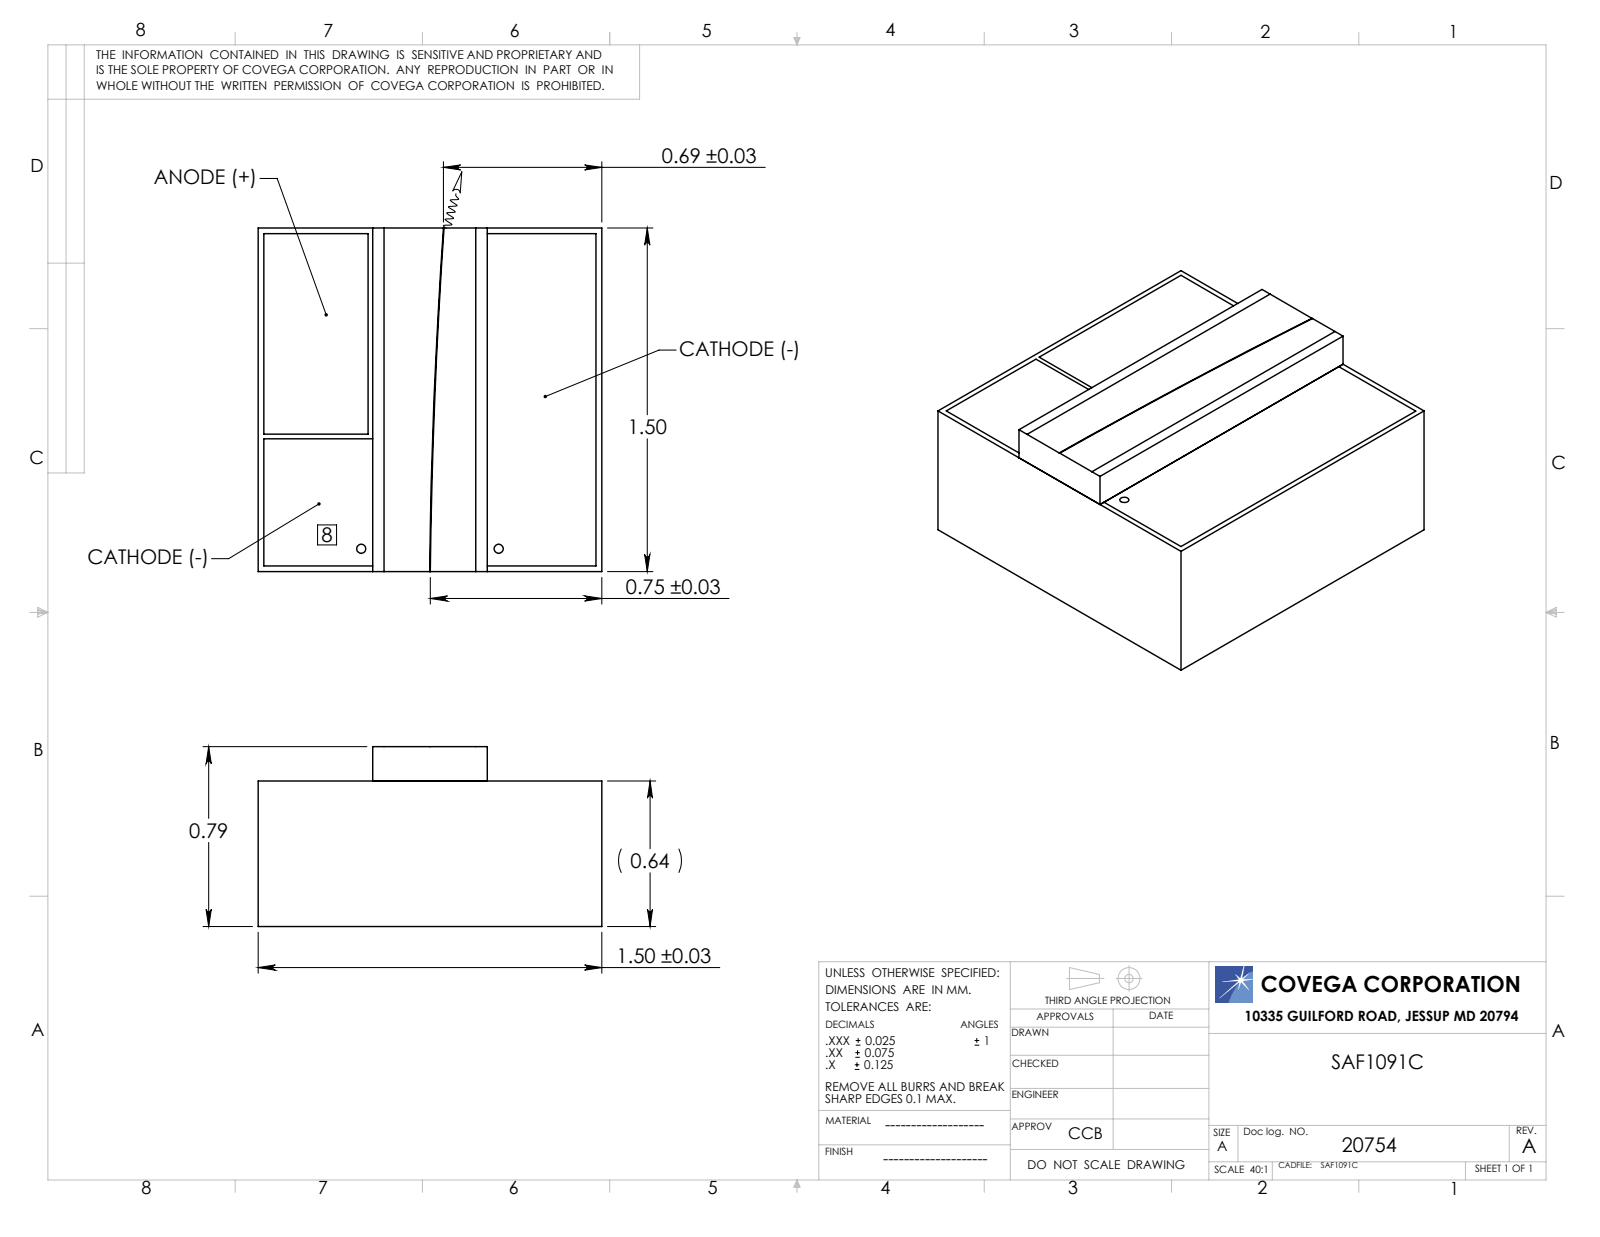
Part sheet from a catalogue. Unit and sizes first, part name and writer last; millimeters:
Units: millimetres
Overall size (bounding box): 1.5 × 1.5 × 0.79
Main face-to-face distances: 0.63, 1.5, 0.78, 0.5, 1
Volume: 2 mm³ · Surface area: 10 mm²
Bodies: 2 solids, 26 faces (26 planar, 0 cylindrical, 0 other)
Part name (STEP PRODUCT): PM-00054; 20754; 31091-XXX
STEP written by: SolidWorks 2009 (CONFIG_CONTROL_DESIGN)
